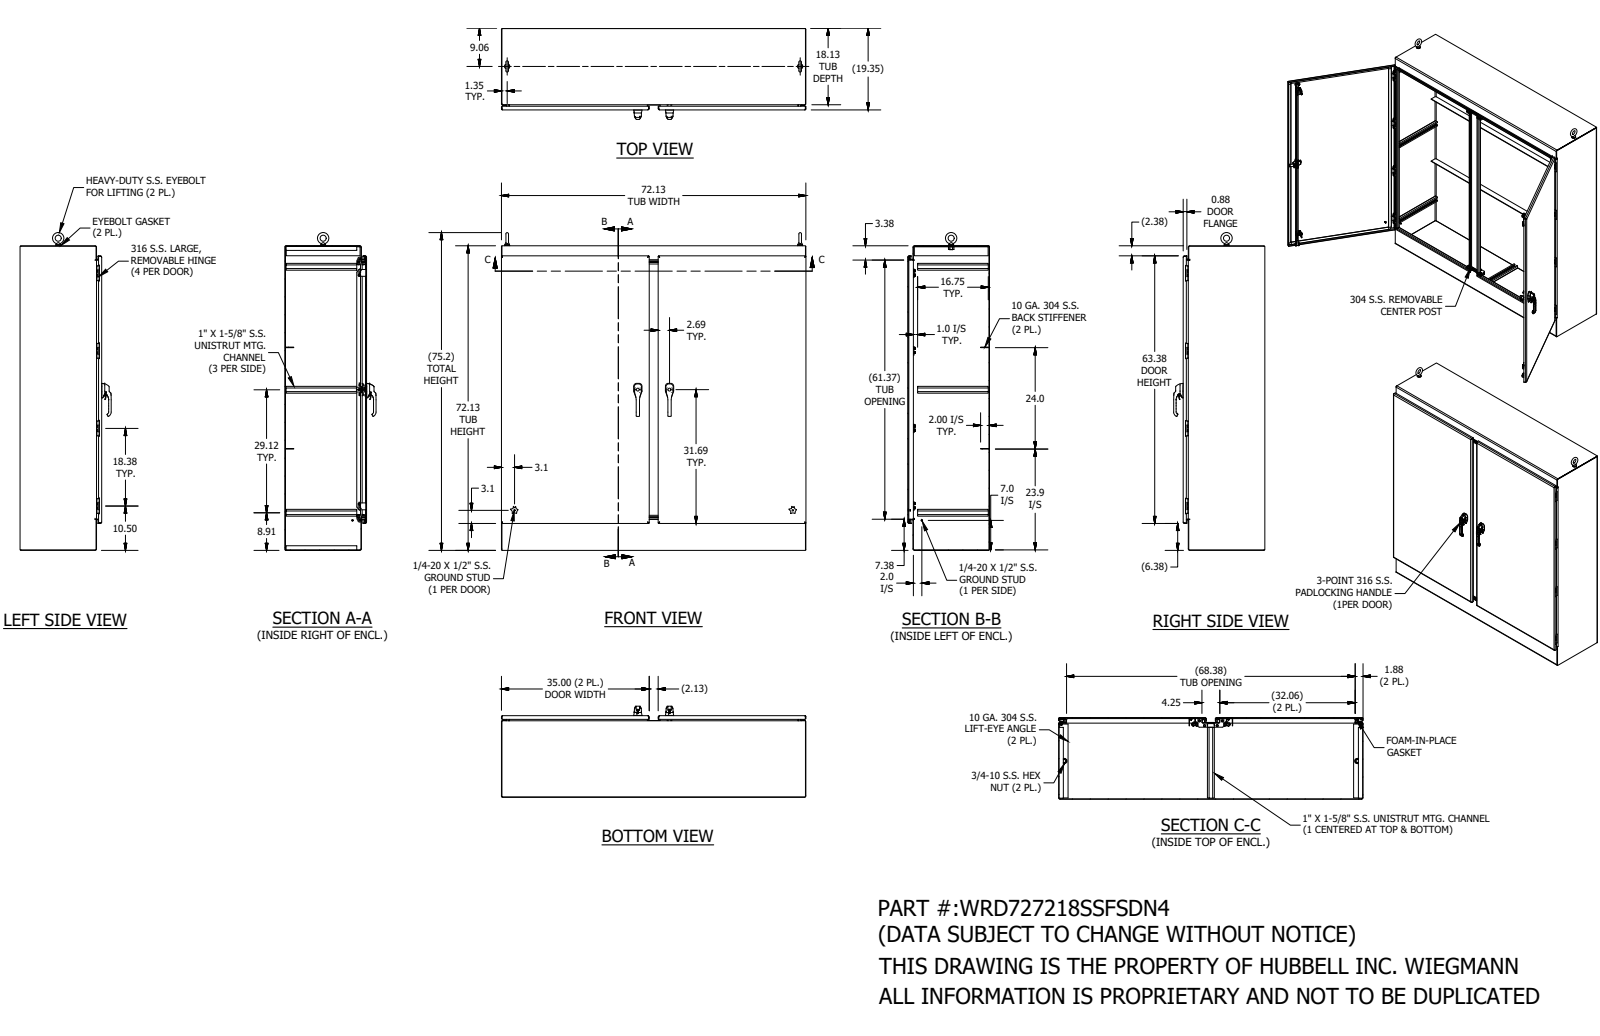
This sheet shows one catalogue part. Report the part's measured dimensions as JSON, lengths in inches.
{"part_name": "WRD727218SSFSDN4; WRD727218SSFSDN4BLR; WRD7218SSFSDN4TOP; WRD7218SSFSDN4BTM (+8 more)", "step_written_by": "Autodesk Inventor 2018 (AUTOMOTIVE_DESIGN)", "units": "inches", "bodies": {"solids": 227, "faces": 9194, "planar": 3894, "cylindrical": 3238, "other": 2062}, "overall_size": [75.248, 72.133, 21.598], "volume_in3": 2062, "surface_area_in2": 38124, "round_holes": [[0.14, 48], [0.266, 20], [0.195, 16], [0.294, 16], [0.65, 16], [0.136, 8], [0.164, 8], [0.187, 8], [0.201, 8], [0.262, 8], [0.213, 6], [0.281, 6]], "round_bosses_or_shafts": [[0.25, 33], [0.625, 16], [0.182, 16], [0.237, 8], [0.236, 6], [1, 4], [0.563, 4], [0.531, 4]], "partial_cylinders_radius": [[0.02, 344], [0.012, 229], [0.062, 64], [0.125, 58], [0.019, 42], [0.079, 28], [0.05, 26], [0.039, 22]], "face_to_face_distances": [0.104, 72.021, 19.245, 19.141, 0.104, 19.349, 19.245, 71.917, 72.125, 18.021], "hole_center_spacings": [8.841, 0.018, 73.218, 0.024, 0.012, 8.719, 1, 18.375]}
